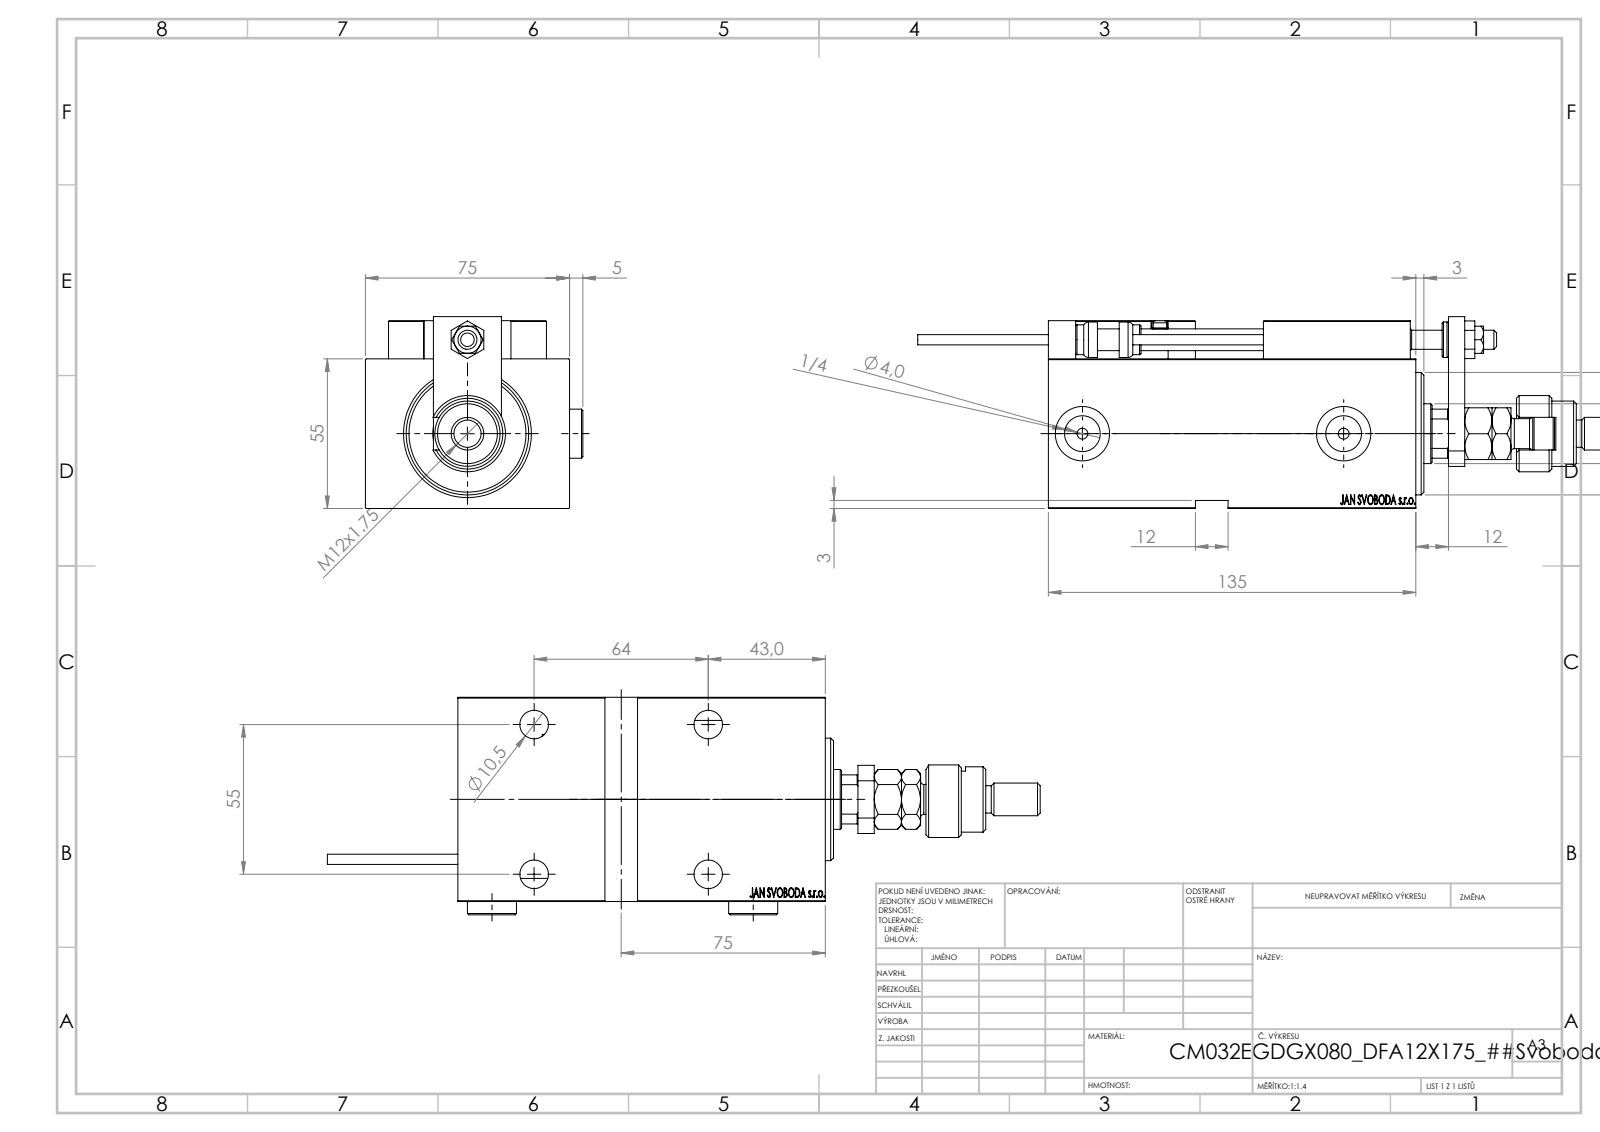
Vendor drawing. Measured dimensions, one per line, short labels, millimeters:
name: ALLEN BOLT D5; FEMALE_PART_FOR_DFA; MFA; KONCOVKA (+8 more)
written by: SolidWorks 2019 (CONFIG_CONTROL_DESIGN)
unit: mm
bodies: 28 solids, 1431 faces (633 planar, 209 cylindrical, 589 other)
size: 262 × 79.9 × 70.5
volume: 565 268 mm³; area: 120 176 mm²
holes: 6× ⌀4, 5× ⌀8, 5× ⌀10.5, 5× ⌀16.5, 4× ⌀3.2, 2× ⌀5, 2× ⌀13.16, 2× ⌀20, 1× ⌀7, 1× ⌀22, 1× ⌀25.5, 1× ⌀32
bosses: 3× ⌀18, 2× ⌀11, 2× ⌀5, 2× ⌀3.8, 1× ⌀34, 1× ⌀28, 1× ⌀24, 1× ⌀13
rounds: 30× R0.3, 2× R3, 1× R9.75, 1× R10.5
face distances: 55, 75, 69, 14, 3, 10, 135, 12, 25, 18
hole spacings: 11.37, 20, 28.9, 29.59, 29.69, 36.06, 40.03, 42.19
